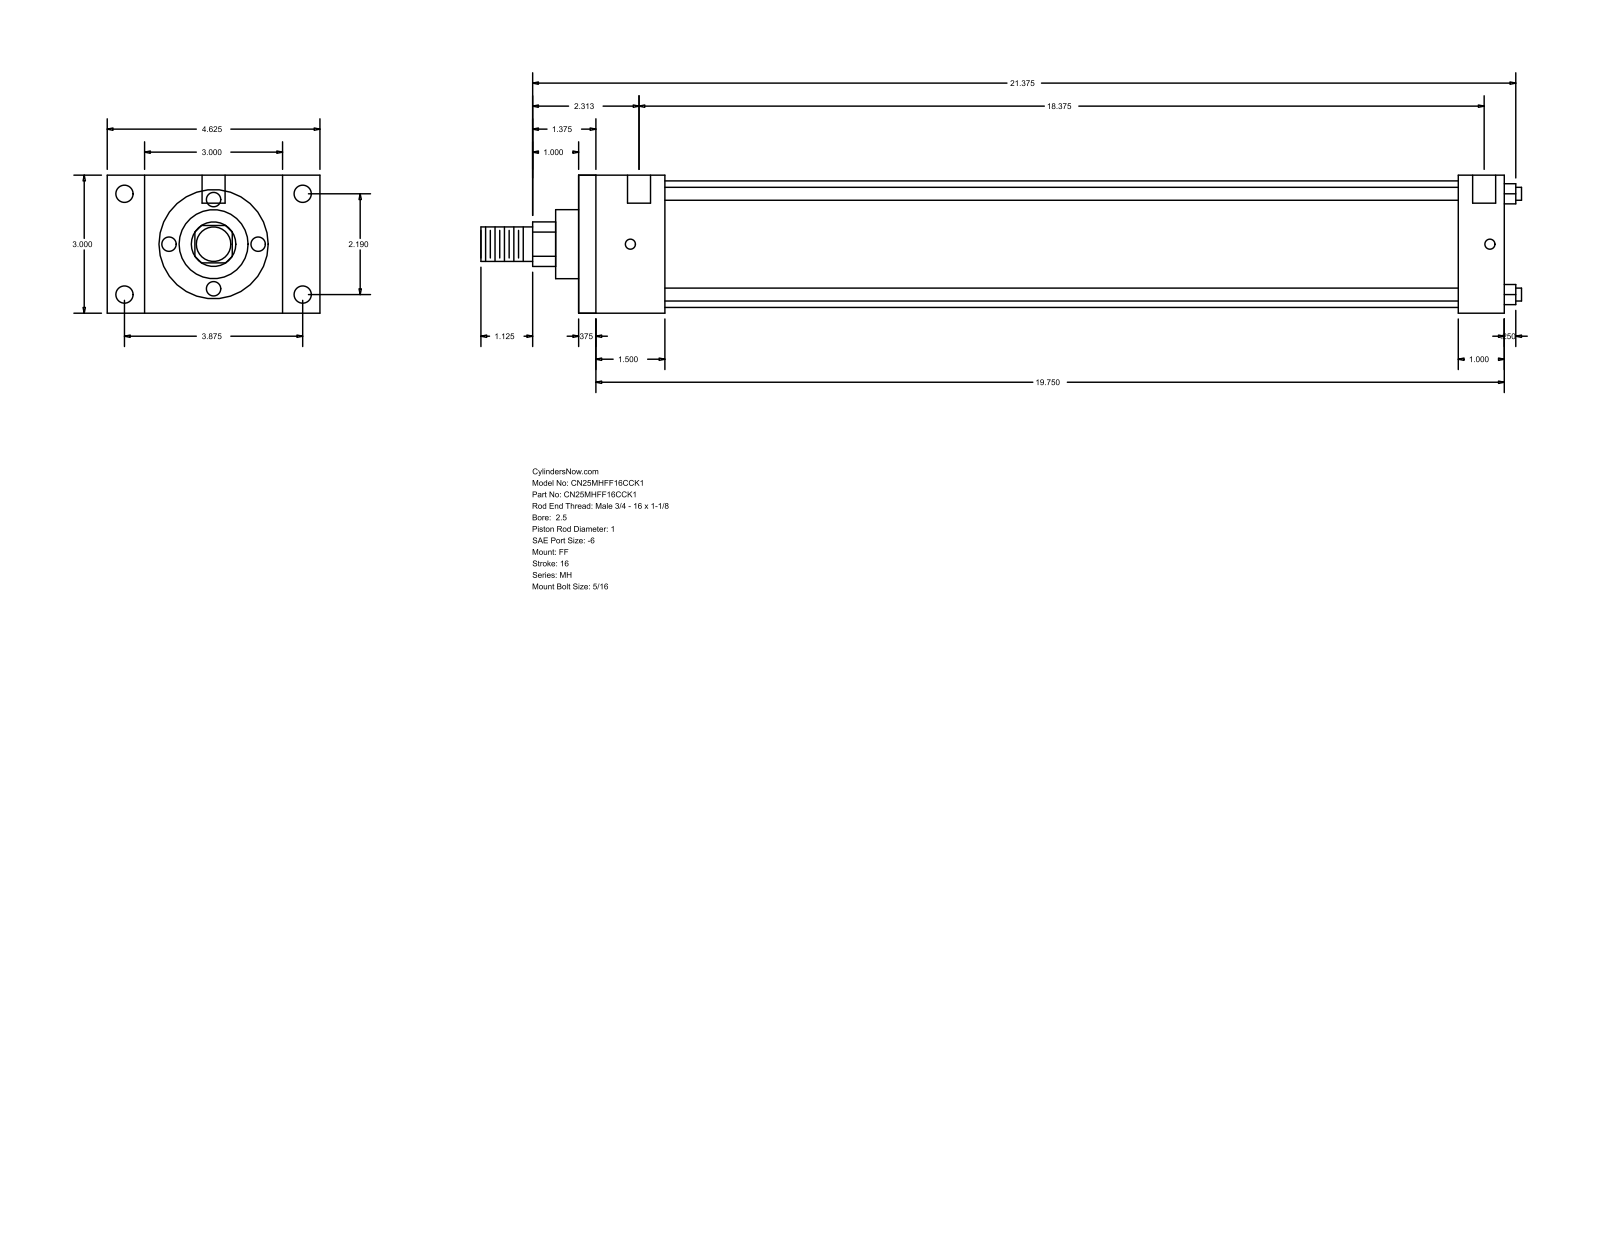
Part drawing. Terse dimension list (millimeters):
name: MH_FF__0250_1
written by: GSSL Pune (CONFIG_CONTROL_DESIGN)
unit: mm
bodies: 0 solids, 92 faces (64 planar, 28 cylindrical, 0 other)
size: 574.67 × 117.47 × 76.2
holes: 4× ⌀5.56, 4× ⌀9.53, 2× ⌀12.7
bosses: 4× ⌀7.14, 1× ⌀69.85, 1× ⌀38.1, 1× ⌀25.4, 1× ⌀19.05
rounds: 1× R12.29
face distances: 76.2, 511.18, 9.52, 501.66, 25.4, 47.63, 485.78, 38.11, 476.26, 438.15
hole spacings: 55.62, 98.42, 113.05, 474.66, 3.18, 4.76, 466.72, 469.9
